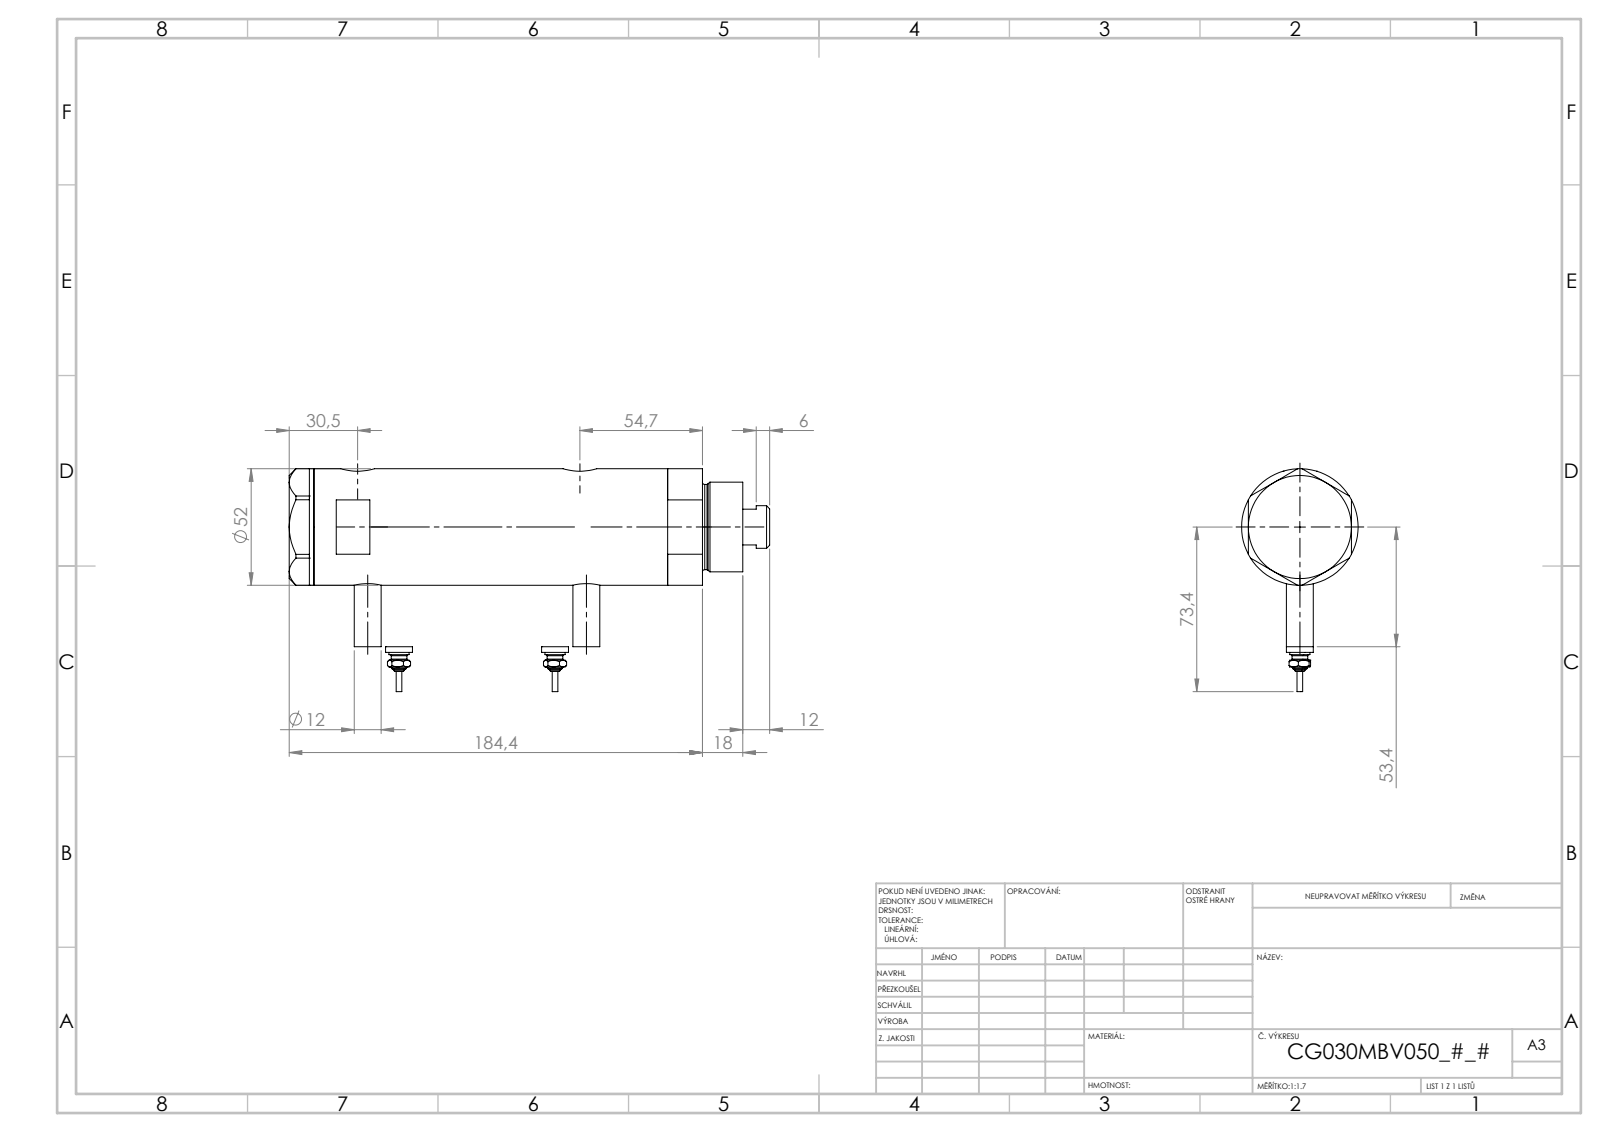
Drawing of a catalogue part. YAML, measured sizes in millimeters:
part_name: "V270CG_FRONT; V270CG_MIDDLE; V270CG_BACK; V270CG_SWITCH (+1 more)"
step_written_by: "SolidWorks 2019 (CONFIG_CONTROL_DESIGN)"
units: millimeters
bodies: {solids: 6, faces: 246, planar: 95, cylindrical: 77, other: 74}
overall_size: [199.02, 84.3, 52]
volume: 356926
surface_area: 83058
round_holes:
  - {diameter: 5, count: 2}
  - {diameter: 9.73, count: 2}
  - {diameter: 12.5, count: 2}
  - {diameter: 15, count: 2}
  - {diameter: 6.5, count: 1}
  - {diameter: 20, count: 1}
  - {diameter: 21.5, count: 1}
  - {diameter: 30, count: 1}
  - {diameter: 33, count: 1}
  - {diameter: 44, count: 1}
round_bosses_or_shafts:
  - {diameter: 12, count: 3}
  - {diameter: 9, count: 2}
  - {diameter: 7, count: 2}
  - {diameter: 4.34, count: 2}
  - {diameter: 2.4, count: 2}
  - {diameter: 52, count: 1}
  - {diameter: 40, count: 1}
  - {diameter: 38, count: 1}
face_to_face_distances: [103.54, 23.8, 79.74, 11, 34.8, 114.54, 46, 150.94, 139.94, 116.14]
hole_center_spacings: [2.9, 4.5, 76.75, 79.65, 81.25, 84.15, 2.89, 2.91]
